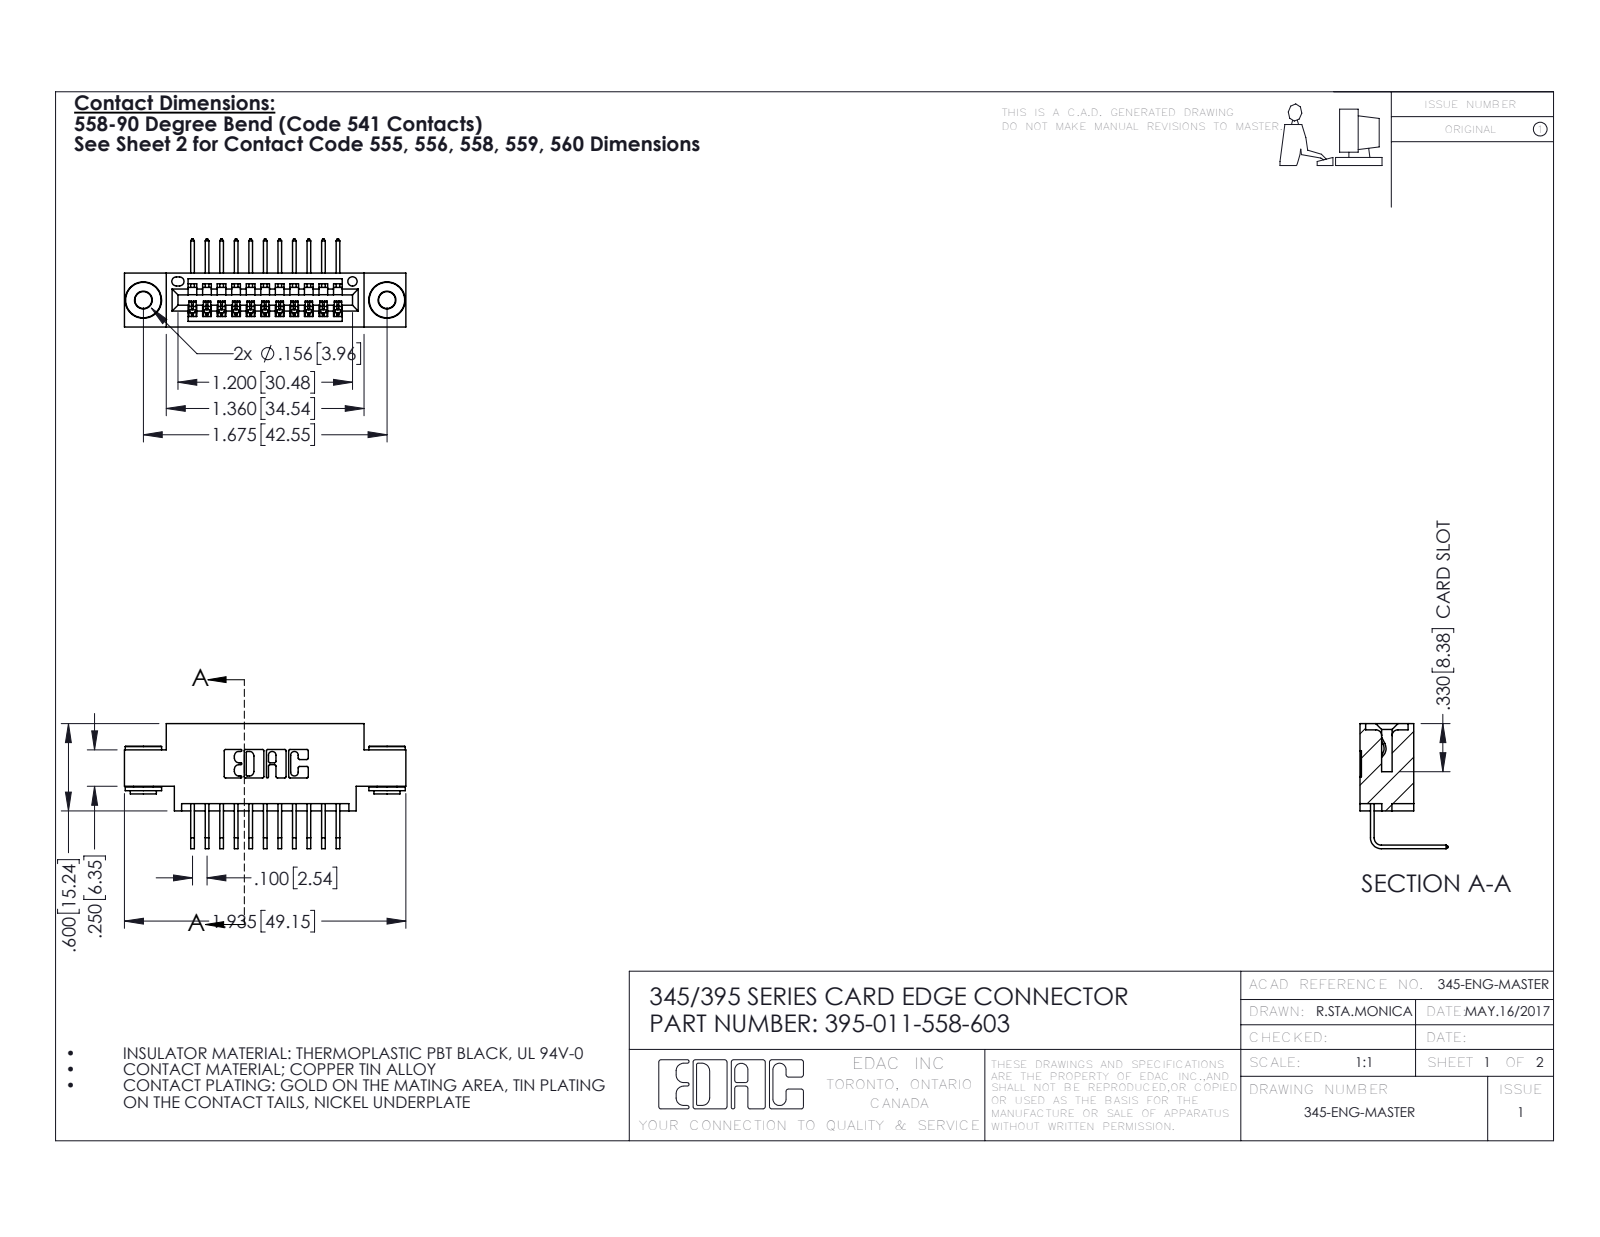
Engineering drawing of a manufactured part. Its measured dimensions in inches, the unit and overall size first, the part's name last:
Units: inches
Overall size (bounding box): 1.935 × 0.859 × 0.605
Round holes (diameter × count): ⌀0.116 ×2, ⌀0.156 ×2, ⌀0.064 ×1
Round bosses / shafts (diameter × count): ⌀0.25 ×2, ⌀0.18 ×2, ⌀0.136 ×2
Partial cylindrical surfaces — rounded edges, fillets, slot ends (radius × count): R0.006 ×22, R0.01 ×22, R0.007 ×6, R0.031 ×6, R0.026 ×3, R0.031 ×2, R0.04 ×2, R0.014 ×1
Main face-to-face distances: 0.37, 0.072, 0.298, 0.2, 0.1, 0.098, 0.272, 0.025, 0.6, 0.225
Hole centre spacings: 0.27, 1.443, 1.675
Volume: 0.266 in³ · Surface area: 9.184 in²
Bodies: 14 solids, 828 faces (556 planar, 264 cylindrical, 8 other)
Part name (STEP PRODUCT): 345-292-001_558 Tail - 2; 345 Part_0.170 Offset - 0.156 Dia-TH; 345-250-002_345-250-002-102; 395-011-558-603
STEP written by: SolidWorks 2016 (CONFIG_CONTROL_DESIGN)
